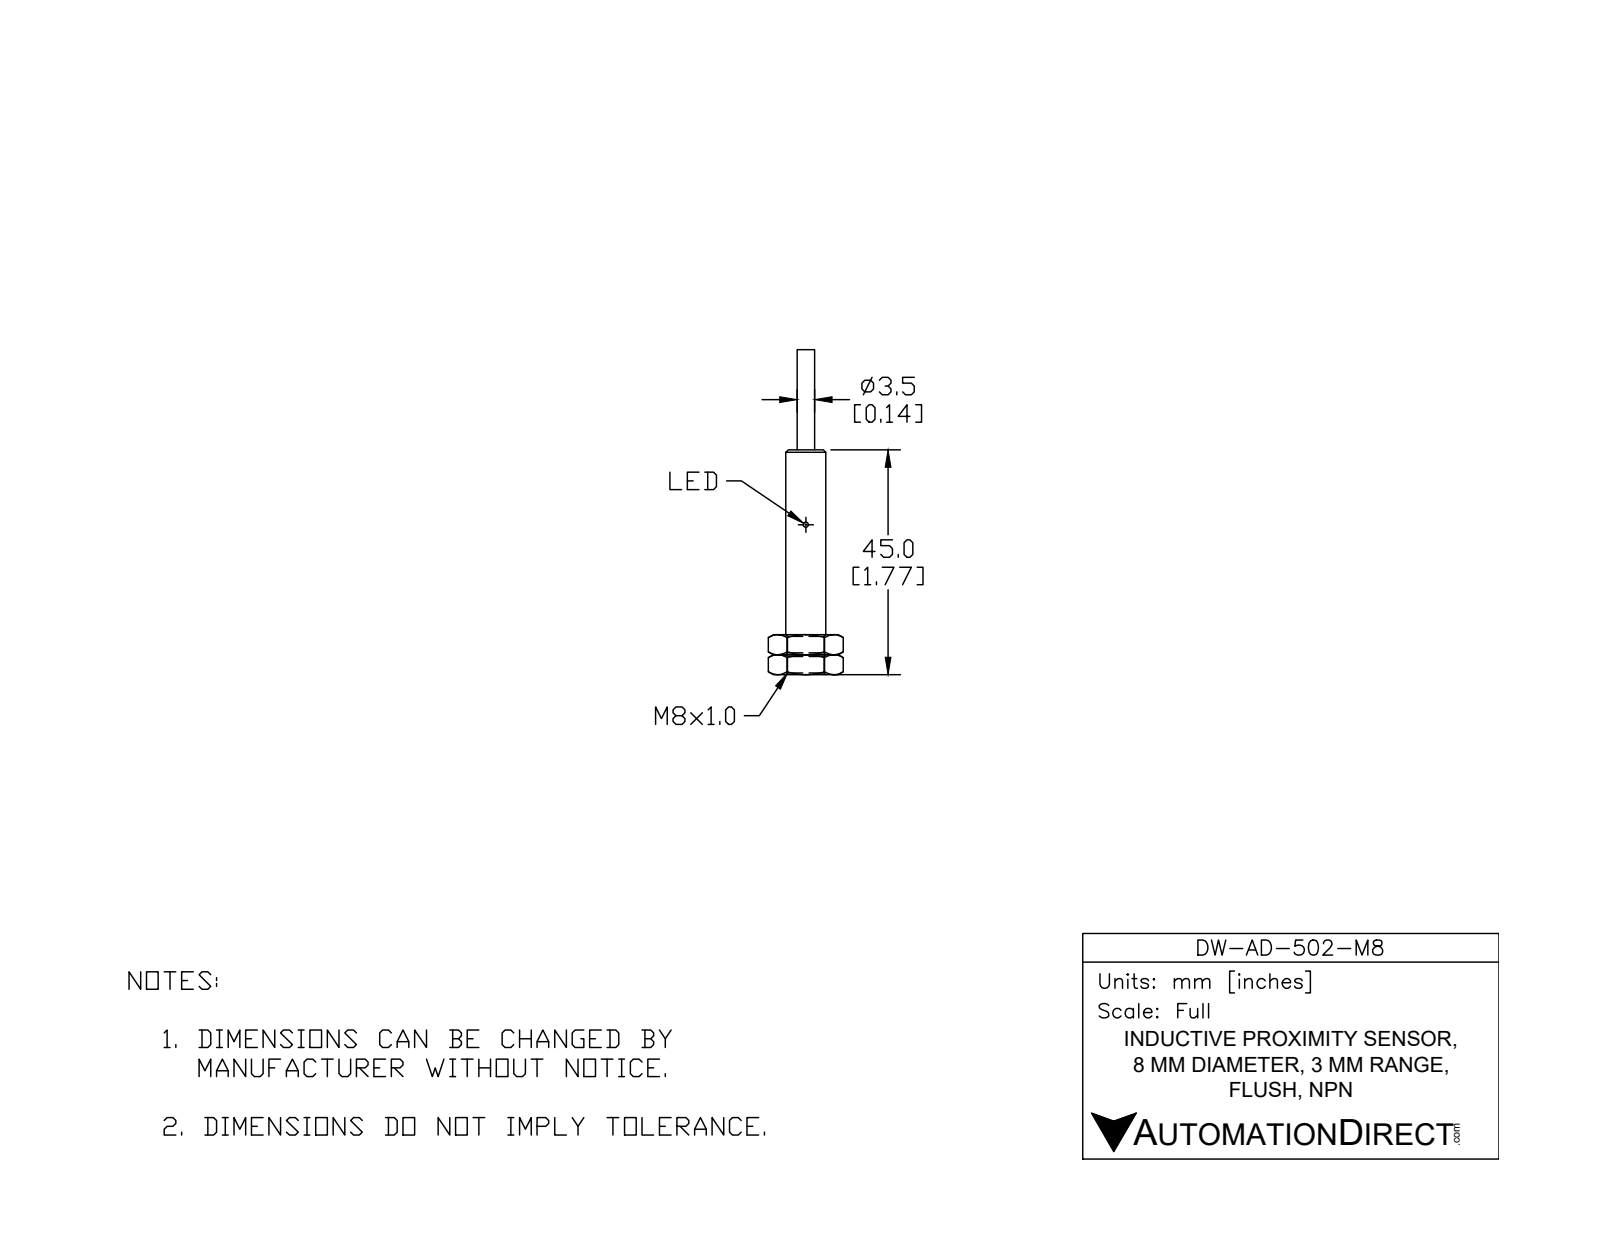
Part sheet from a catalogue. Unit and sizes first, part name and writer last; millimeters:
Units: millimetres
Overall size (bounding box): 71.2 × 8 × 8
Round bosses / shafts (diameter × count): ⌀8 ×1, ⌀6.5 ×1, ⌀5 ×1
Main face-to-face distances: 71.2, 45.5, 25.7, 45, 0.5, 26.2
Volume: 2 790 mm³ · Surface area: 1 632 mm²
Bodies: 1 solid, 10 faces (4 planar, 3 cylindrical, 3 other)
Part name (STEP PRODUCT): DW-AD-502-M8
STEP written by: SolidWorks 2017 (AUTOMOTIVE_DESIGN)
